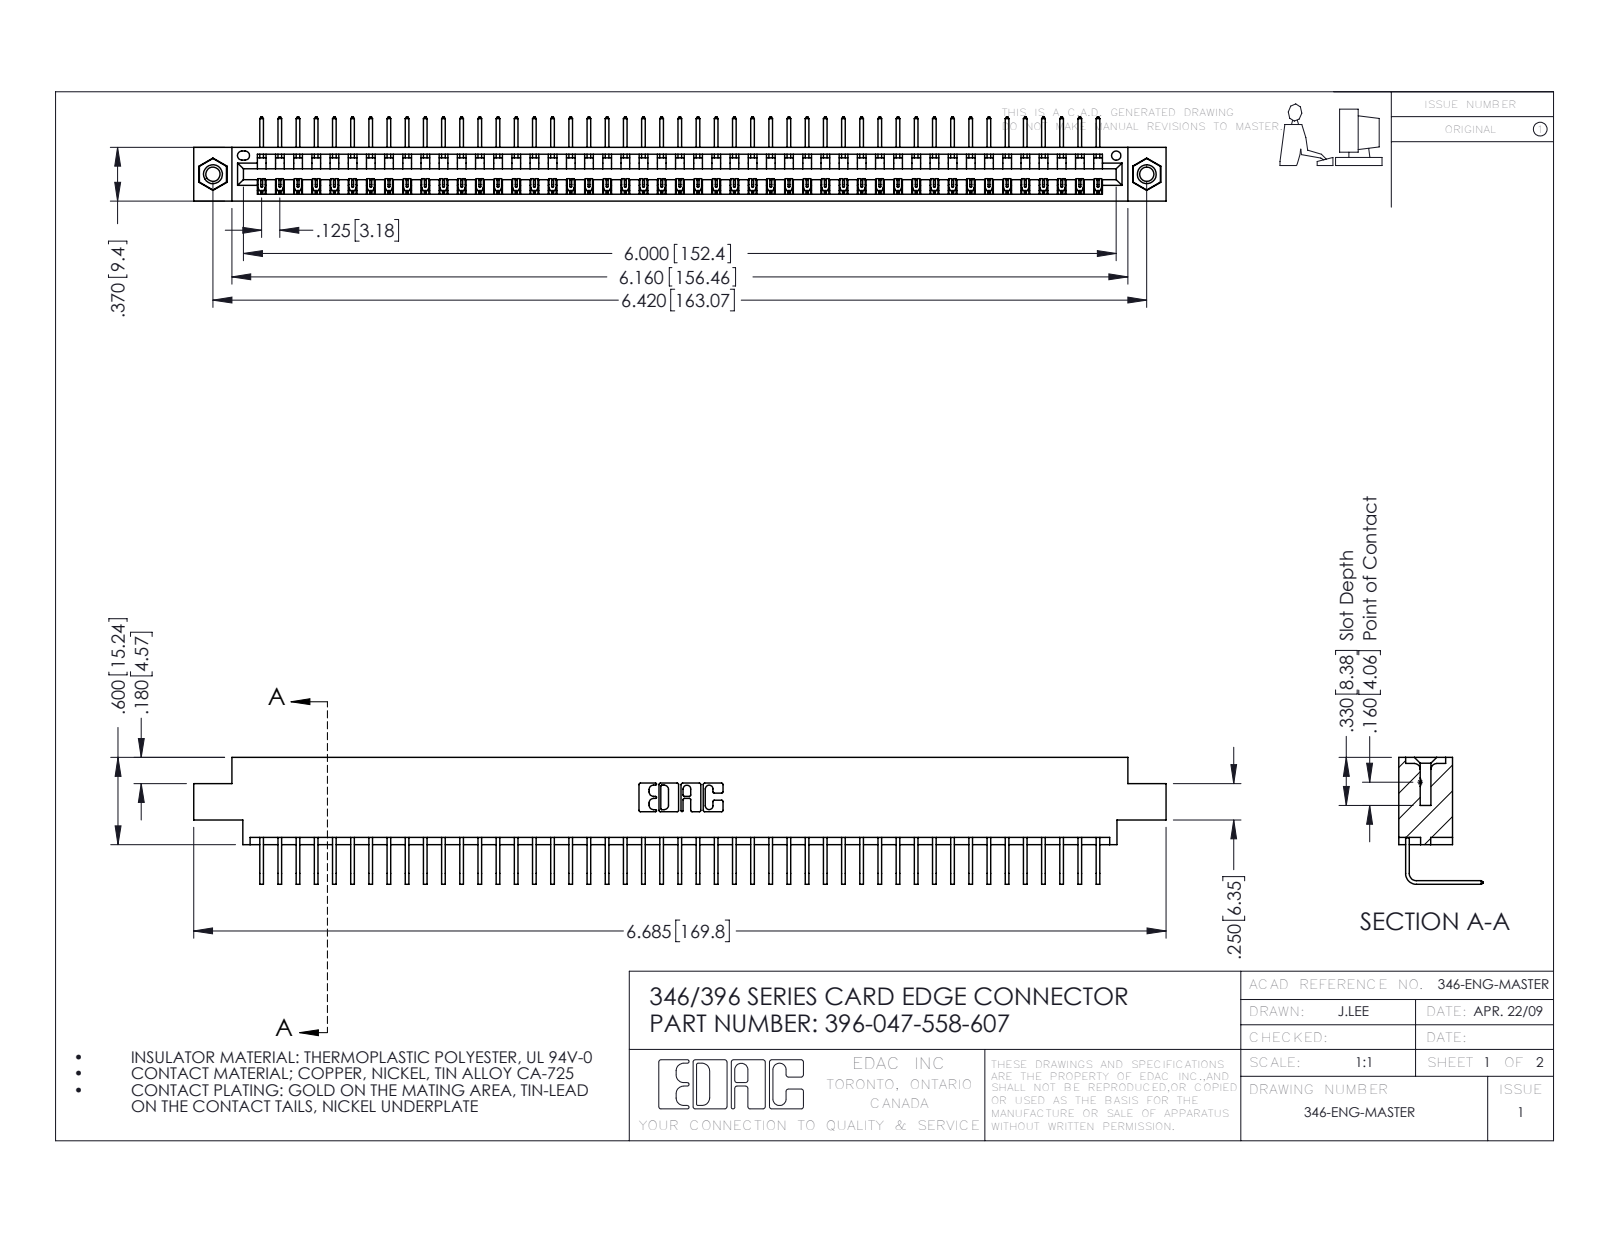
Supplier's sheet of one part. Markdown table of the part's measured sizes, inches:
| quantity | value |
| --- | --- |
| part name | 396-047-558-607; 346 Part_0.170 Offset - 0.156 Dia-TI; 345-250-001_345-250-005-103; 345-292-001_558 Tail - 2 |
| STEP written by | SolidWorks 2016 (CONFIG_CONTROL_DESIGN) |
| units | inches |
| bodies | 50 solids, 3006 faces (2086 planar, 904 cylindrical, 16 other) |
| overall size | 6.685 × 0.873 × 0.58 |
| volume | 0.993 in³ |
| surface area | 33.37 in² |
| round holes (diameter × count) | 0.098 × 2, 0.125 × 2, 0.156 × 2, 0.064 × 1 |
| round bosses / shafts (diameter × count) | 0.155 × 2 |
| partial cylindrical surfaces (radius × count) | 0.006 × 94, 0.01 × 22, 0.007 × 6, 0.031 × 6, 0.026 × 3, 0.031 × 2, 0.04 × 2, 0.014 × 1 |
| main face-to-face distances | 0.322, 0.048, 0.37, 0.25, 0.298, 0.025, 0.072, 0.222, 0.148, 0.1 |
| hole center spacings | 0.246, 6.211, 6.42 |
